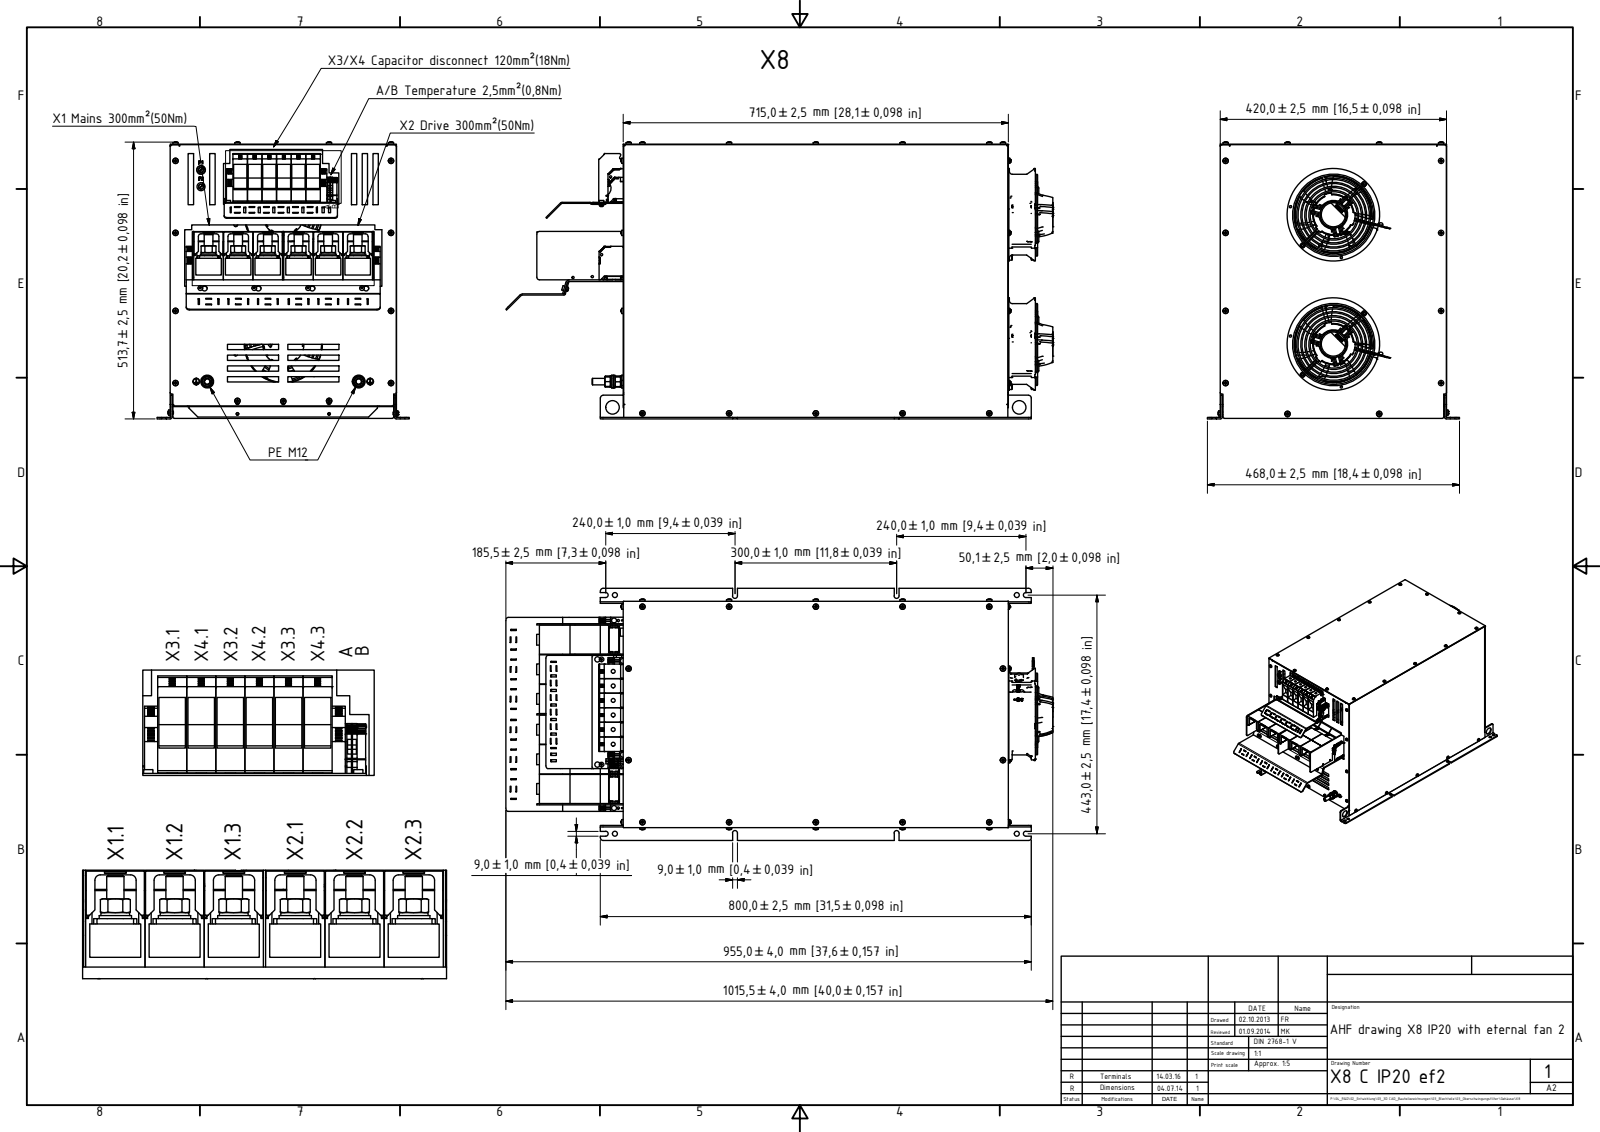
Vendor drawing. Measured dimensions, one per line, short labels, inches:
name: 10100531 Seitenwand X8-A1; 10100530 Lüfterblech X8-A1; 10100529 Anschlussblech X8-A1; DIN 7985 (Z) - M5x6-Z (+8 more)
written by: Autodesk Inventor 2015 (AUTOMOTIVE_DESIGN)
unit: in
bodies: 157 solids, 16187 faces (9608 planar, 2852 cylindrical, 3727 other)
size: 39.159 × 20.231 × 18.425
volume: 429.7 in³; area: 8 533 in²
holes: 41× ⌀0.256, 36× ⌀0.163, 20× ⌀0.128, 16× ⌀0.276, 9× ⌀0.157, 6× ⌀0.197, 6× ⌀0.394, 4× ⌀0.156, 4× ⌀0.167, 4× ⌀0.217, 4× ⌀0.335, 4× ⌀0.354
bosses: 41× ⌀0.197, 37× ⌀0.181, 14× ⌀0.63, 12× ⌀1.181, 12× ⌀1.051, 12× ⌀0.098, 10× ⌀0.335, 4× ⌀0.039
rounds: 412× R0.02, 154× R0.012, 152× R0.033, 114× R0.039, 64× R0.012, 61× R0.004, 54× R0.128, 47× R0.079
face distances: 0.039, 16.496, 16.457, 16.535, 0.118, 28.11, 0.079, 19.016, 19.055, 19.134
hole spacings: 3.937, 5.268, 10.969, 15.748, 6.339, 0.295, 7.874, 12.677
